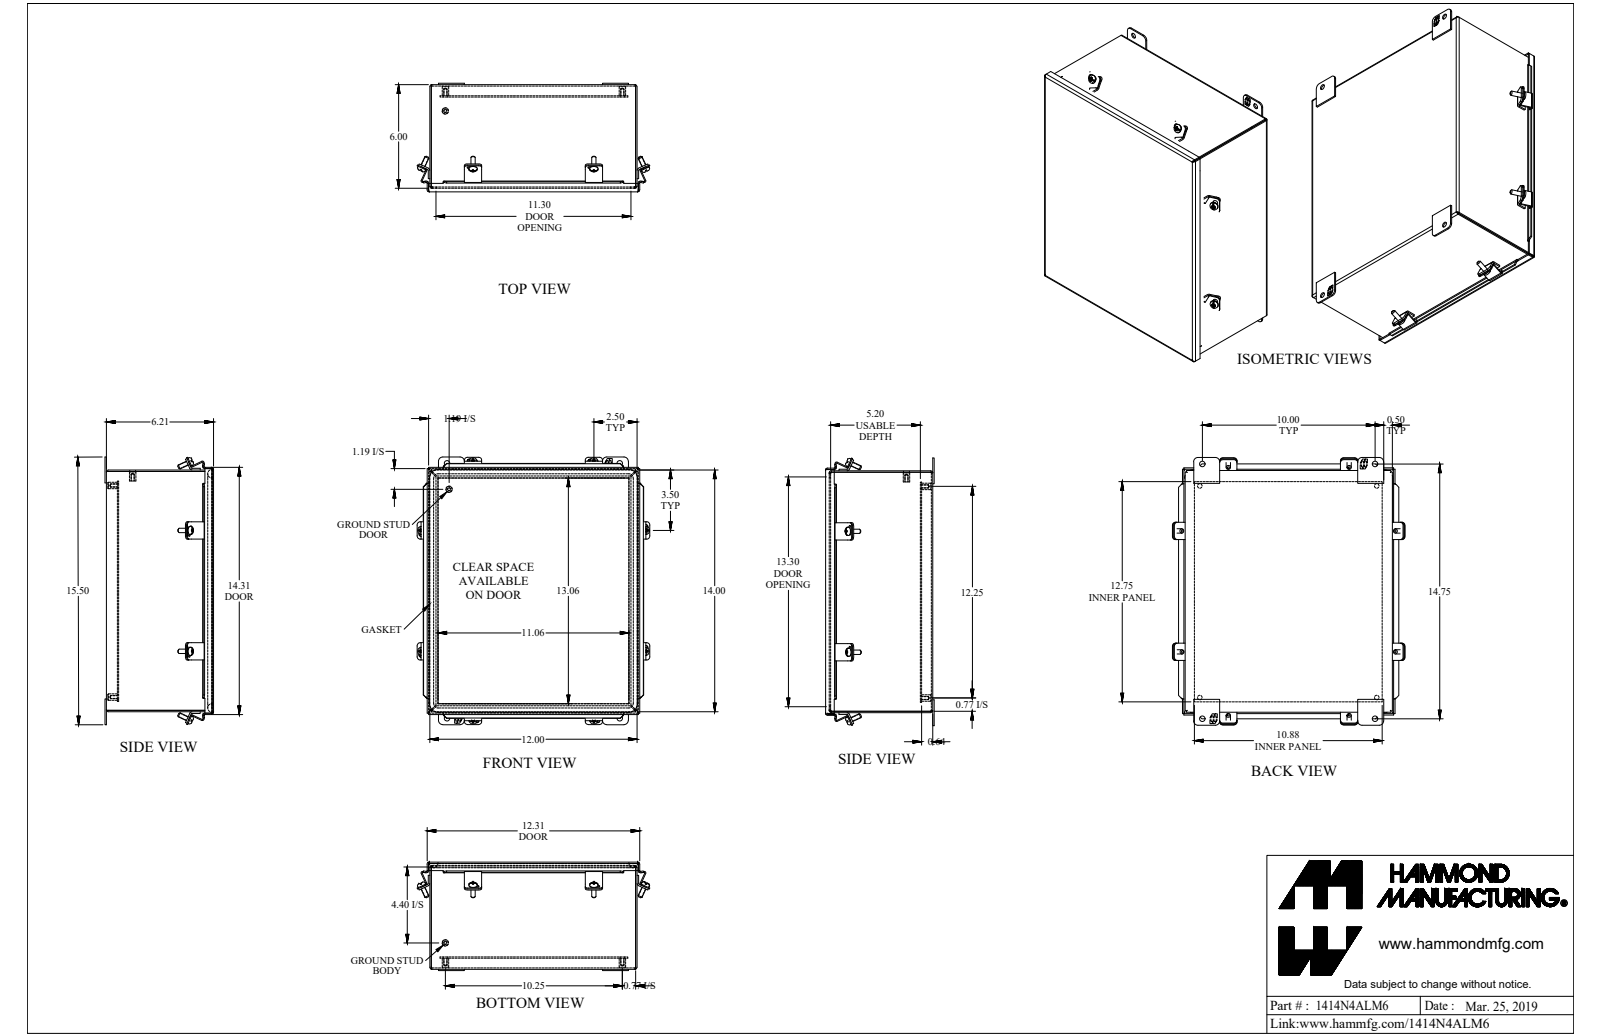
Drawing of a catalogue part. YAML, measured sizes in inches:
part_name: "1414N4ALM6"
step_written_by: "SolidWorks 2018 (AUTOMOTIVE_DESIGN)"
units: inches
bodies: {solids: 38, faces: 1051, planar: 719, cylindrical: 238, other: 94}
overall_size: [15.5, 13.475, 6.286]
volume: 73.85
surface_area: 1875
round_holes:
  - {diameter: 0.213, count: 8}
  - {diameter: 0.159, count: 6}
  - {diameter: 0.265, count: 4}
  - {diameter: 0.313, count: 4}
round_bosses_or_shafts:
  - {diameter: 0.48, count: 8}
  - {diameter: 0.25, count: 8}
  - {diameter: 0.375, count: 6}
  - {diameter: 0.33, count: 6}
partial_cylinders:
  - {radius: 0.188, count: 32}
  - {radius: 0.141, count: 16}
  - {radius: 0.25, count: 12}
  - {radius: 0.01, count: 10}
  - {radius: 0.029, count: 8}
  - {radius: 0.036, count: 8}
  - {radius: 0.048, count: 8}
  - {radius: 0.086, count: 8}
face_to_face_distances: [0.081, 6.125, 6.206, 6.044, 11.919, 0.562, 0.643, 5.563, 5.482, 5.491]
hole_center_spacings: [7, 10, 10.25, 12.25, 14.75, 15.972, 17.82, 0.31]
